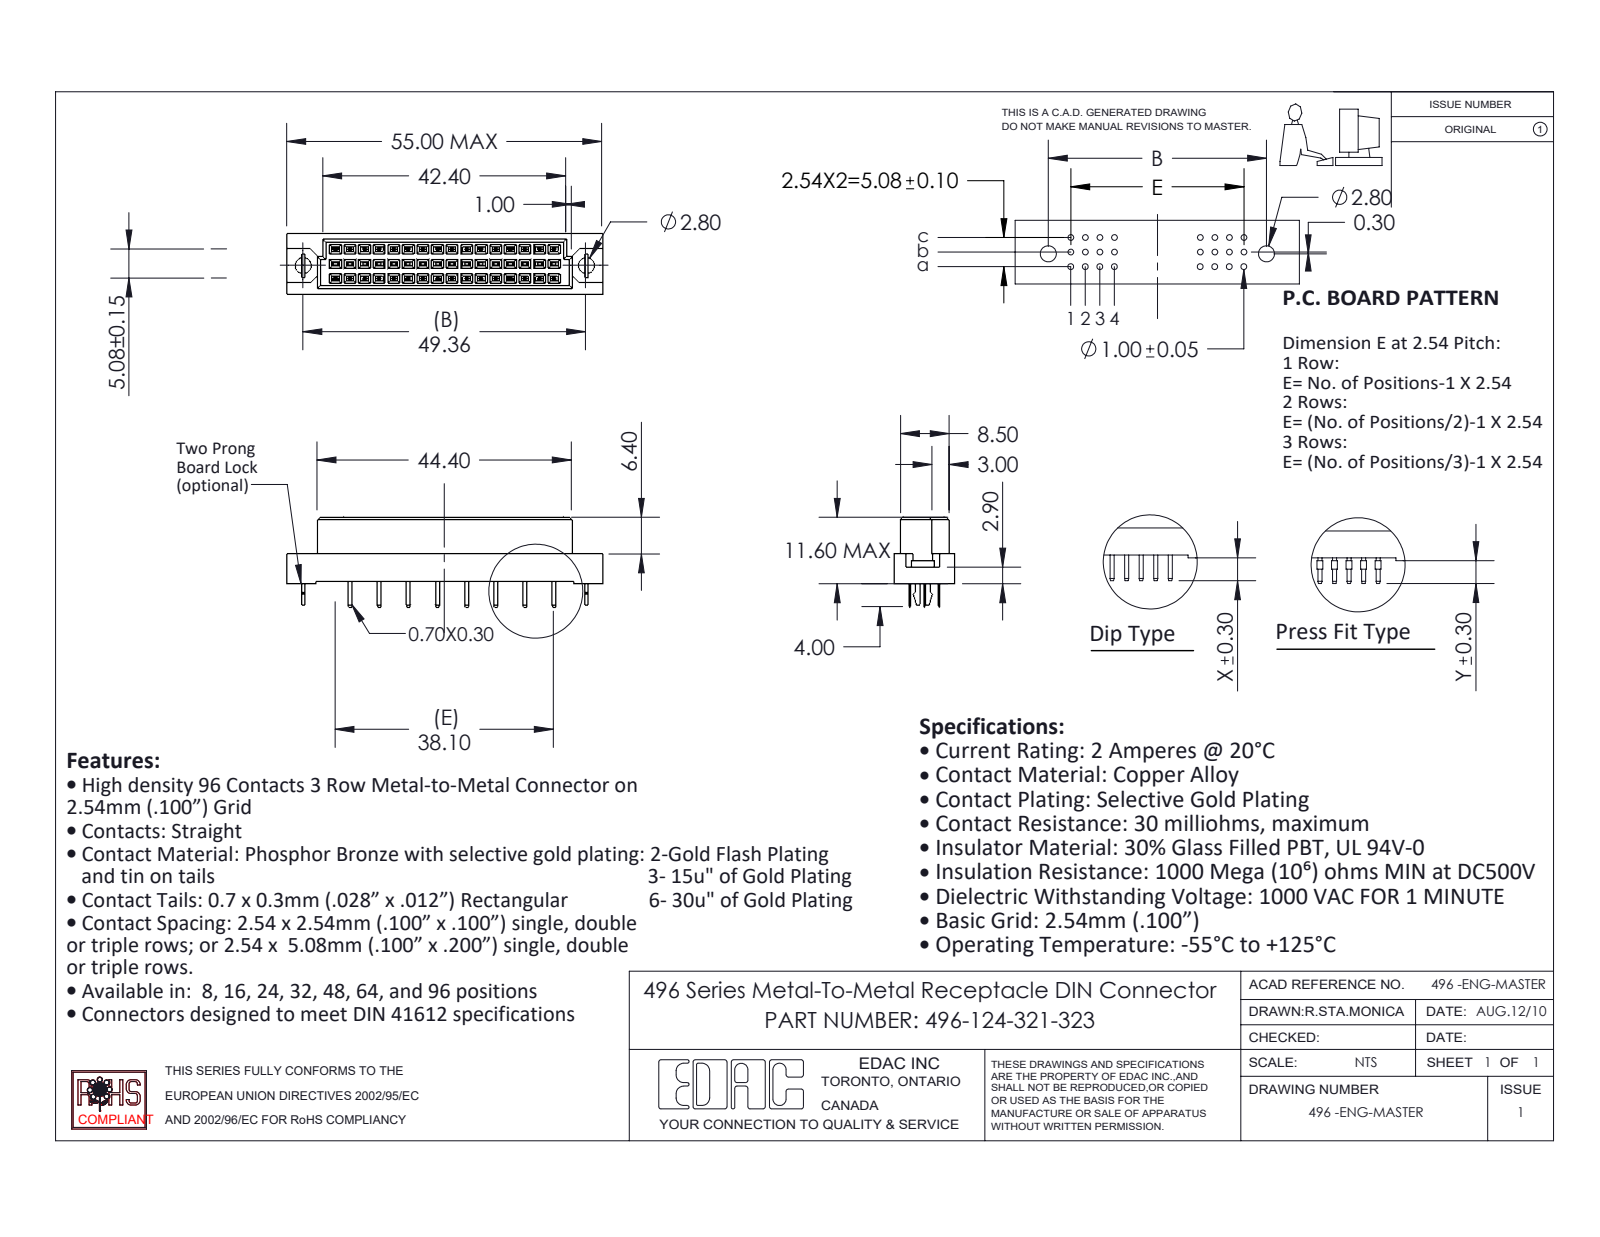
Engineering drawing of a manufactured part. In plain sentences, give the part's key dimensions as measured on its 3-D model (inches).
The part is named "496 Part_48; 496 Bore-lock; 496-124-321-323; 496-290_21". Its 3-D file was written by "SolidWorks 2020 (CONFIG_CONTROL_DESIGN)". It is 27 solids with 942 faces: 936 planar, 6 cylindrical and 0 other. Overall it measures 2.165 by 0.614 by 0.417 inches. Its volume is 0.284 cubic inches and its surface area 7.335 square inches. Round holes: 2 of diameter 0.11. Partial cylindrical surfaces (rounded edges, fillets, slot ends): 1 of radius 0.021. The main face-to-face distances are 0.1, 0.2, 0.041, 0.376, 0.032, 0.022, 0.022, 0.417, 0.132, 0.068. The hole center spacings are 1.943.
